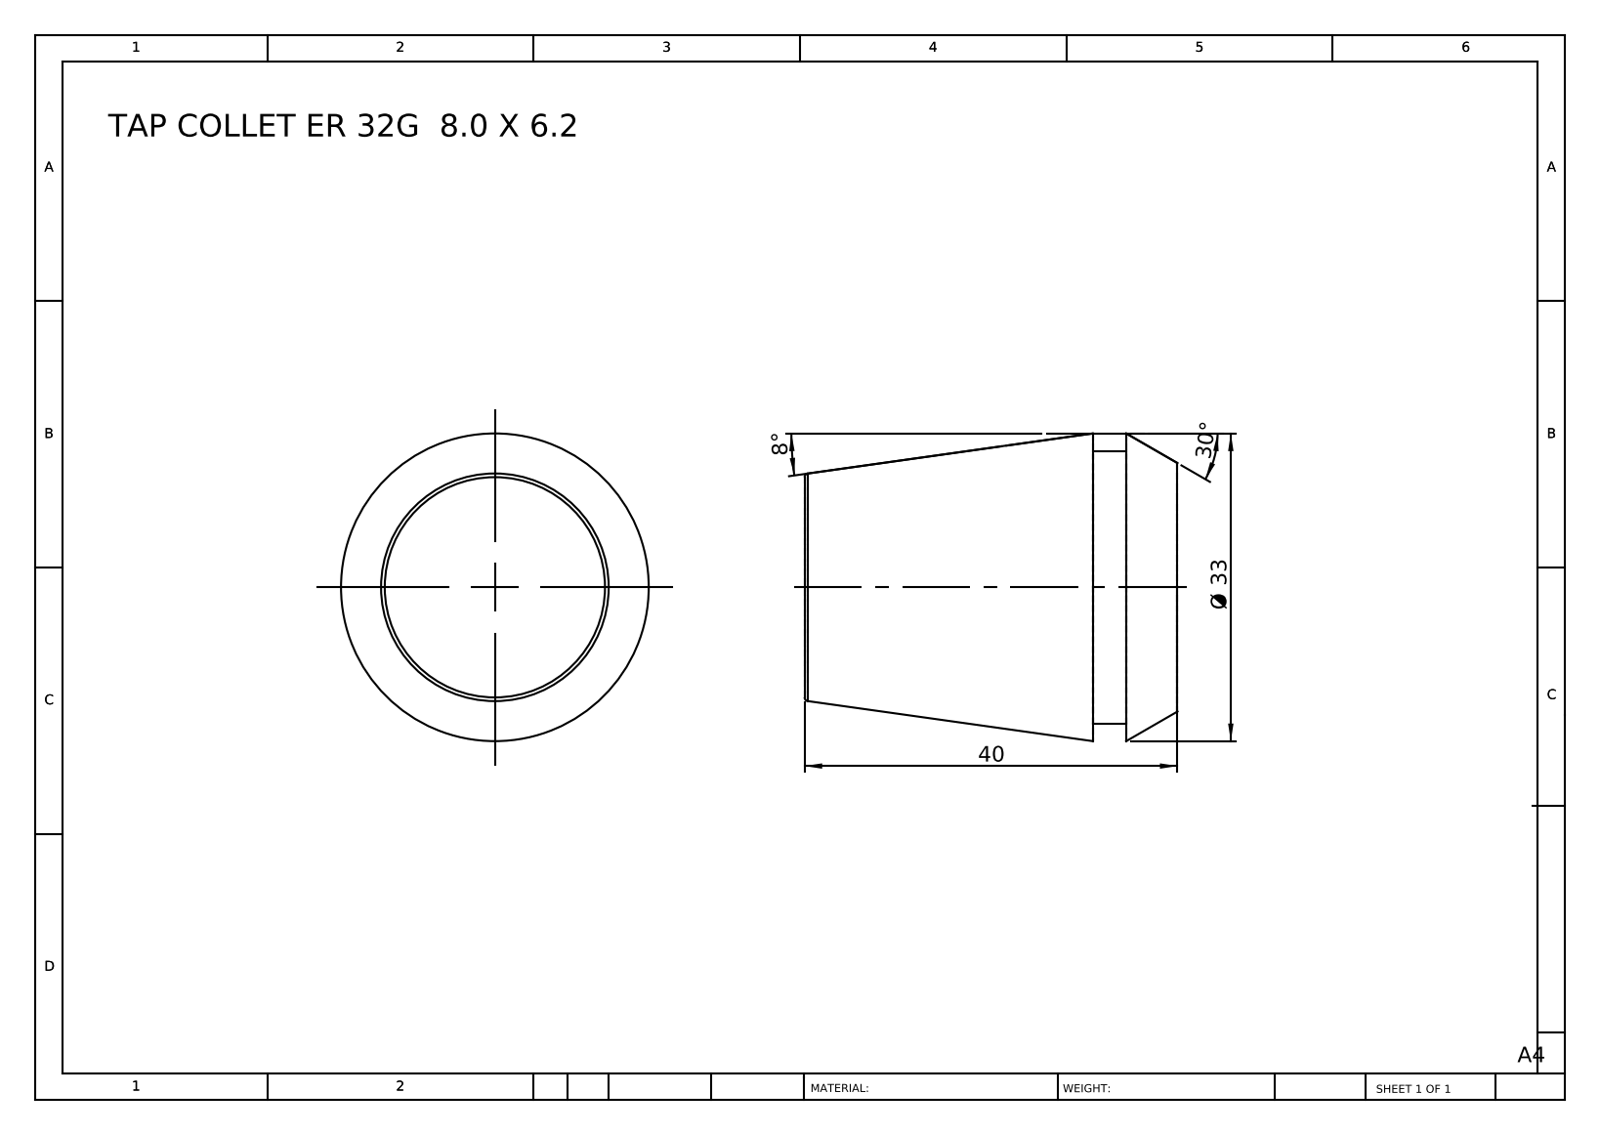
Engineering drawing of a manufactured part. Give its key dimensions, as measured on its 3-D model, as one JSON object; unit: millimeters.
{"part_name": "TAP COLLET ER 32G 8.0 X 6.3", "step_written_by": "SolidWorks 2014 (CONFIG_CONTROL_DESIGN)", "units": "millimeters", "bodies": {"solids": 1, "faces": 12, "planar": 4, "cylindrical": 2, "other": 6}, "overall_size": [40, 33, 33], "volume_mm3": 26350, "surface_area_mm2": 5119, "round_bosses_or_shafts": [[29.2, 1]], "face_to_face_distances": [40, 9.1, 30.9, 5.5, 3.6, 34.5]}
